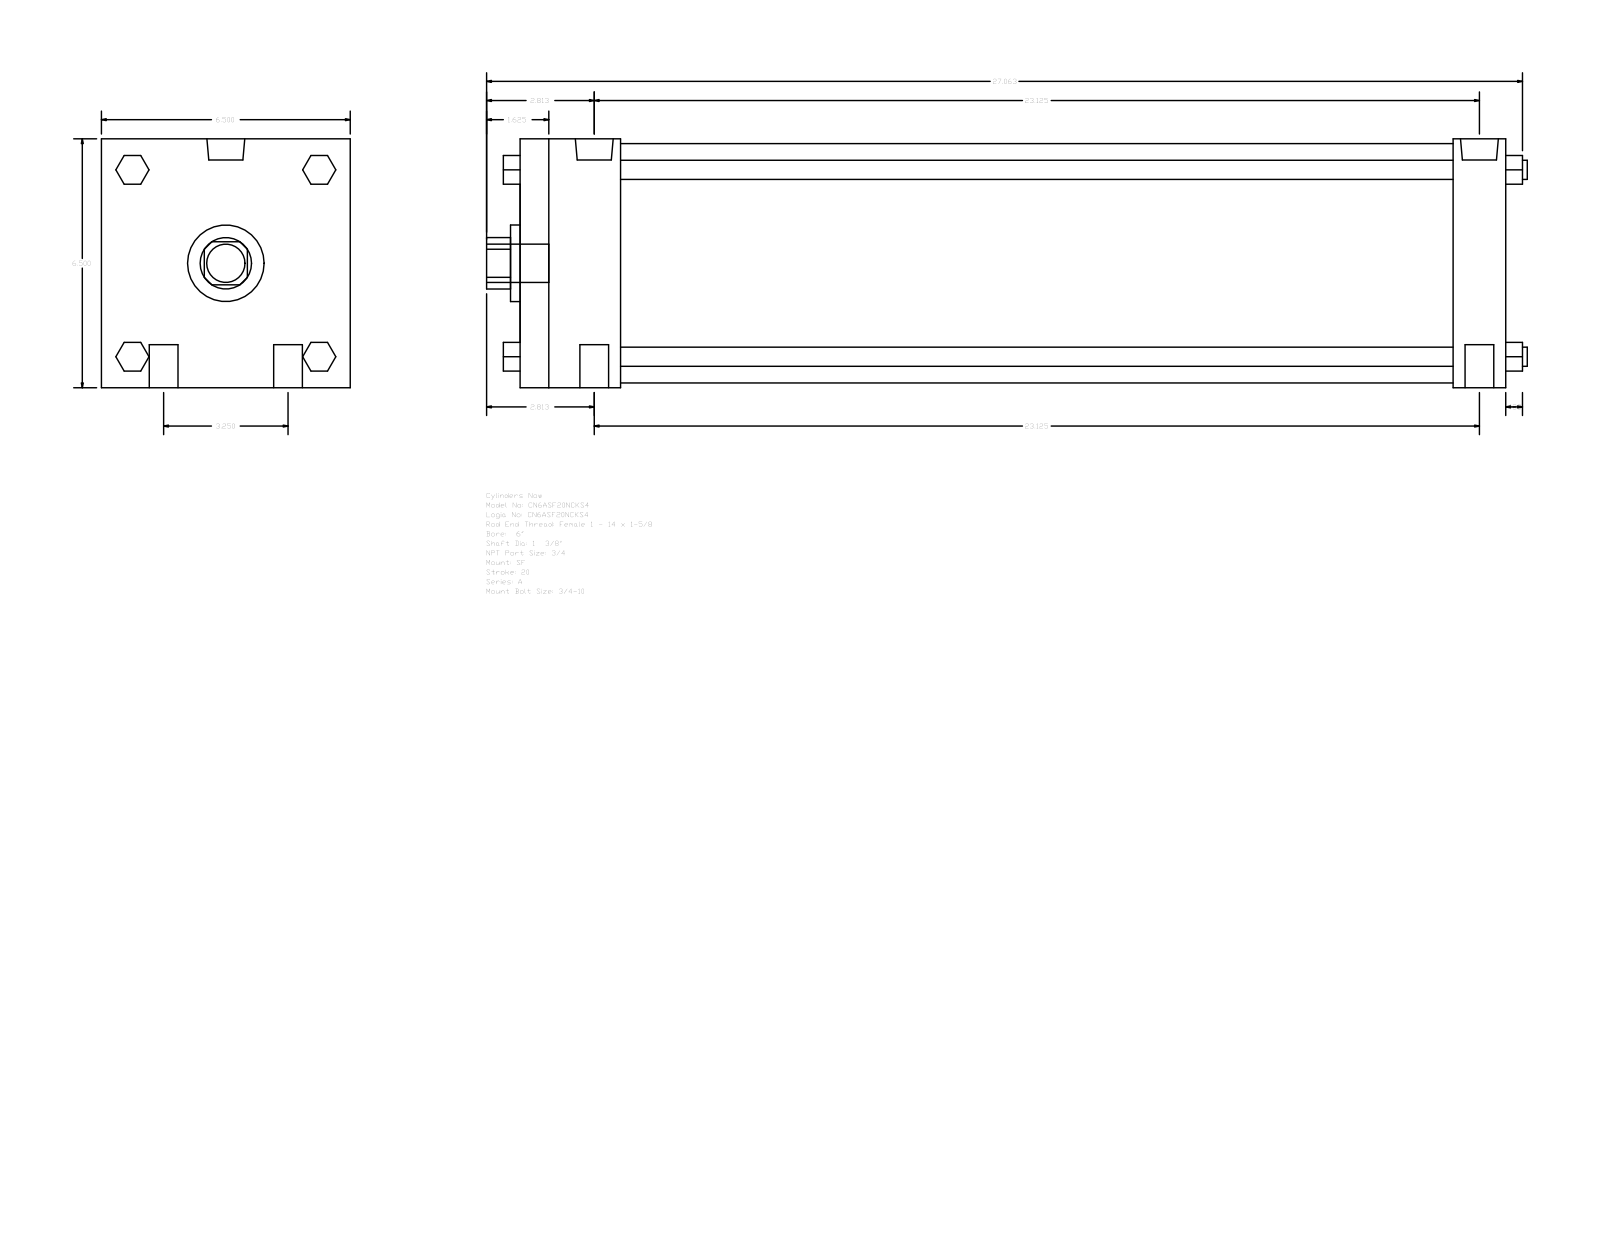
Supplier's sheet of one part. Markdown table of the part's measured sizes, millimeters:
| quantity | value |
| --- | --- |
| part name | A_SF__0600_1.375 |
| STEP written by | GSSL Pune (CONFIG_CONTROL_DESIGN) |
| units | millimeters |
| bodies | 0 solids, 124 faces (94 planar, 30 cylindrical, 0 other) |
| overall size | 690.56 × 165.1 × 165.1 |
| round holes (diameter × count) | 34.92 × 1, 50.8 × 1, 158.75 × 1 |
| round bosses / shafts (diameter × count) | 19.05 × 4, 12.7 × 4, 25.12 × 2, 15.08 × 2, 25.4 × 1 |
| partial cylindrical surfaces (radius × count) | 17.06 × 1 |
| main face-to-face distances | 165.1, 654.04, 619.12, 34.92, 66.67, 552.45, 587.37, 19.05, 61.97, 107.34 |
